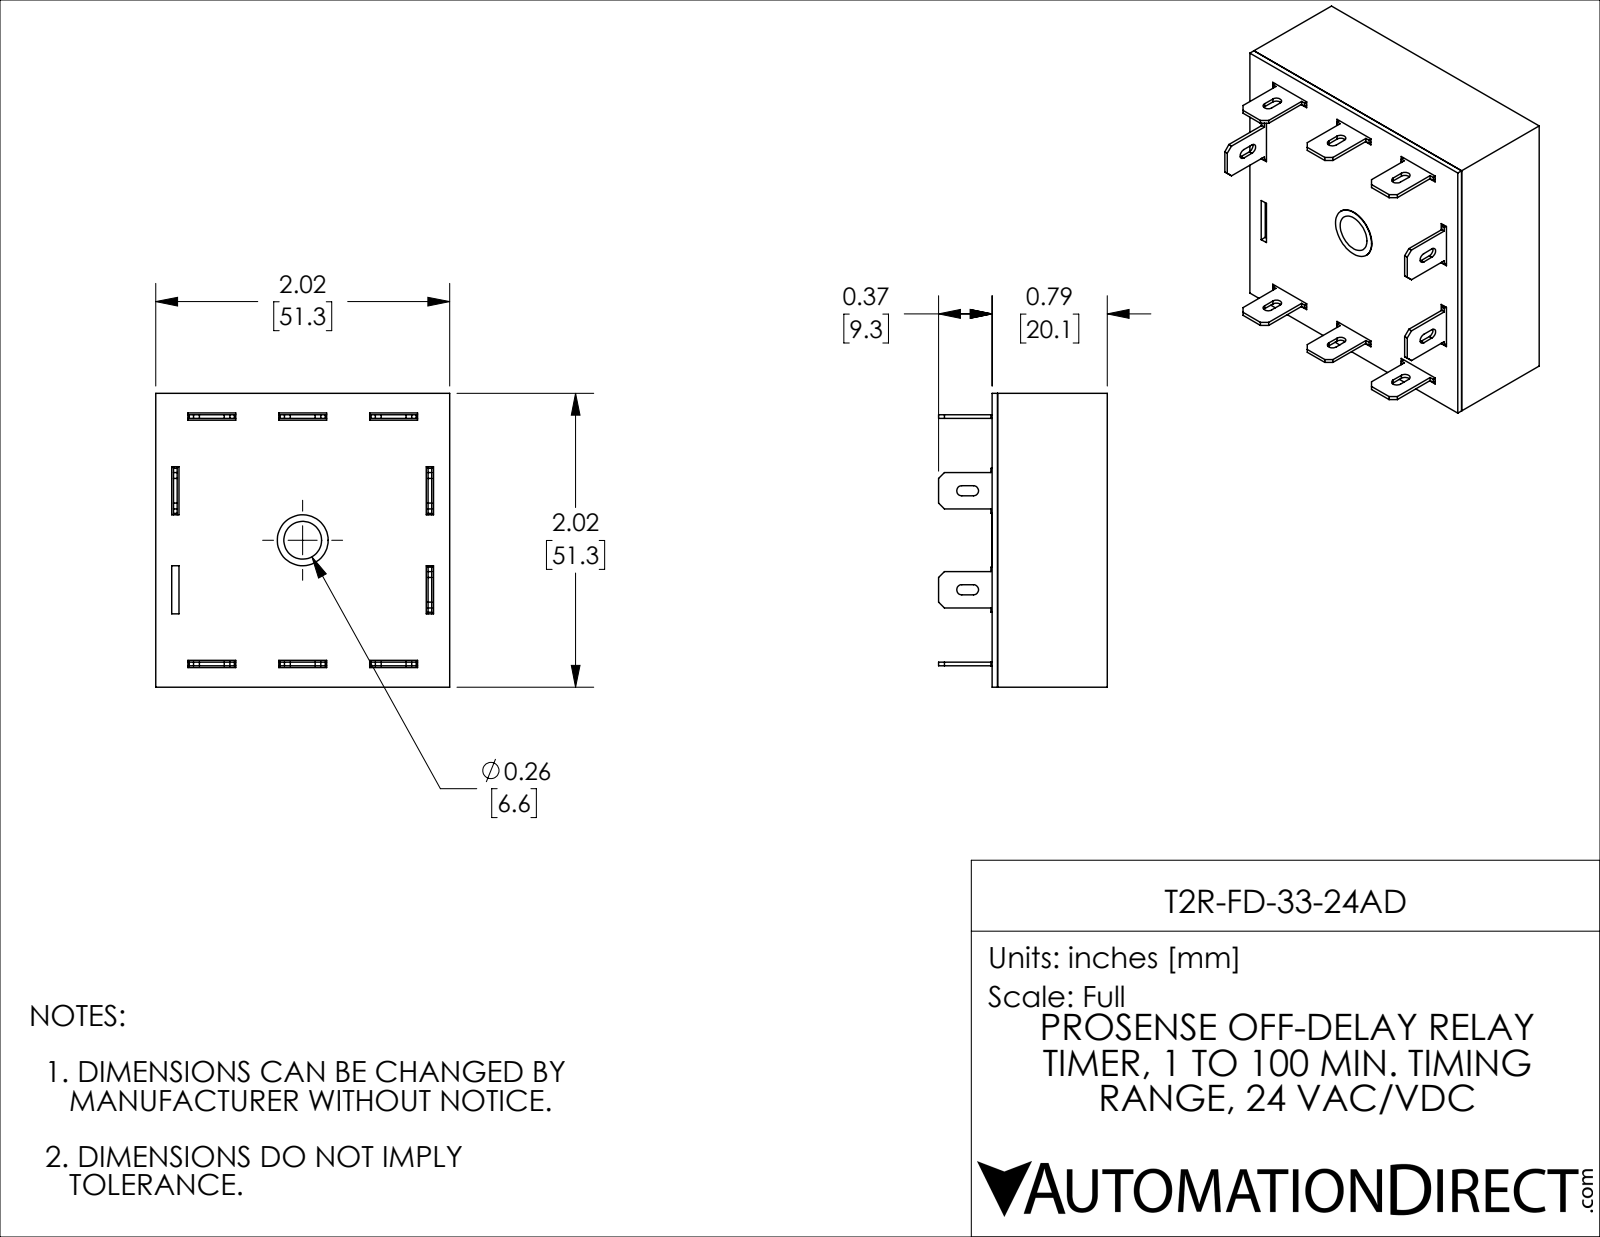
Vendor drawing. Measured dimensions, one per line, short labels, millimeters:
name: T2R-FD-33-24AD
written by: SolidWorks 2021 (CONFIG_CONTROL_DESIGN)
unit: mm
bodies: 11 solids, 280 faces (256 planar, 22 cylindrical, 2 other)
size: 51.31 × 51.31 × 29.46
volume: 11 178 mm³; area: 23 301 mm²
holes: 1× ⌀8.89
rounds: 10× R0.89
face distances: 1.14, 50.16, 19.15, 20.12, 0.97, 18.01, 18.98, 51.3, 3.74, 47.56
